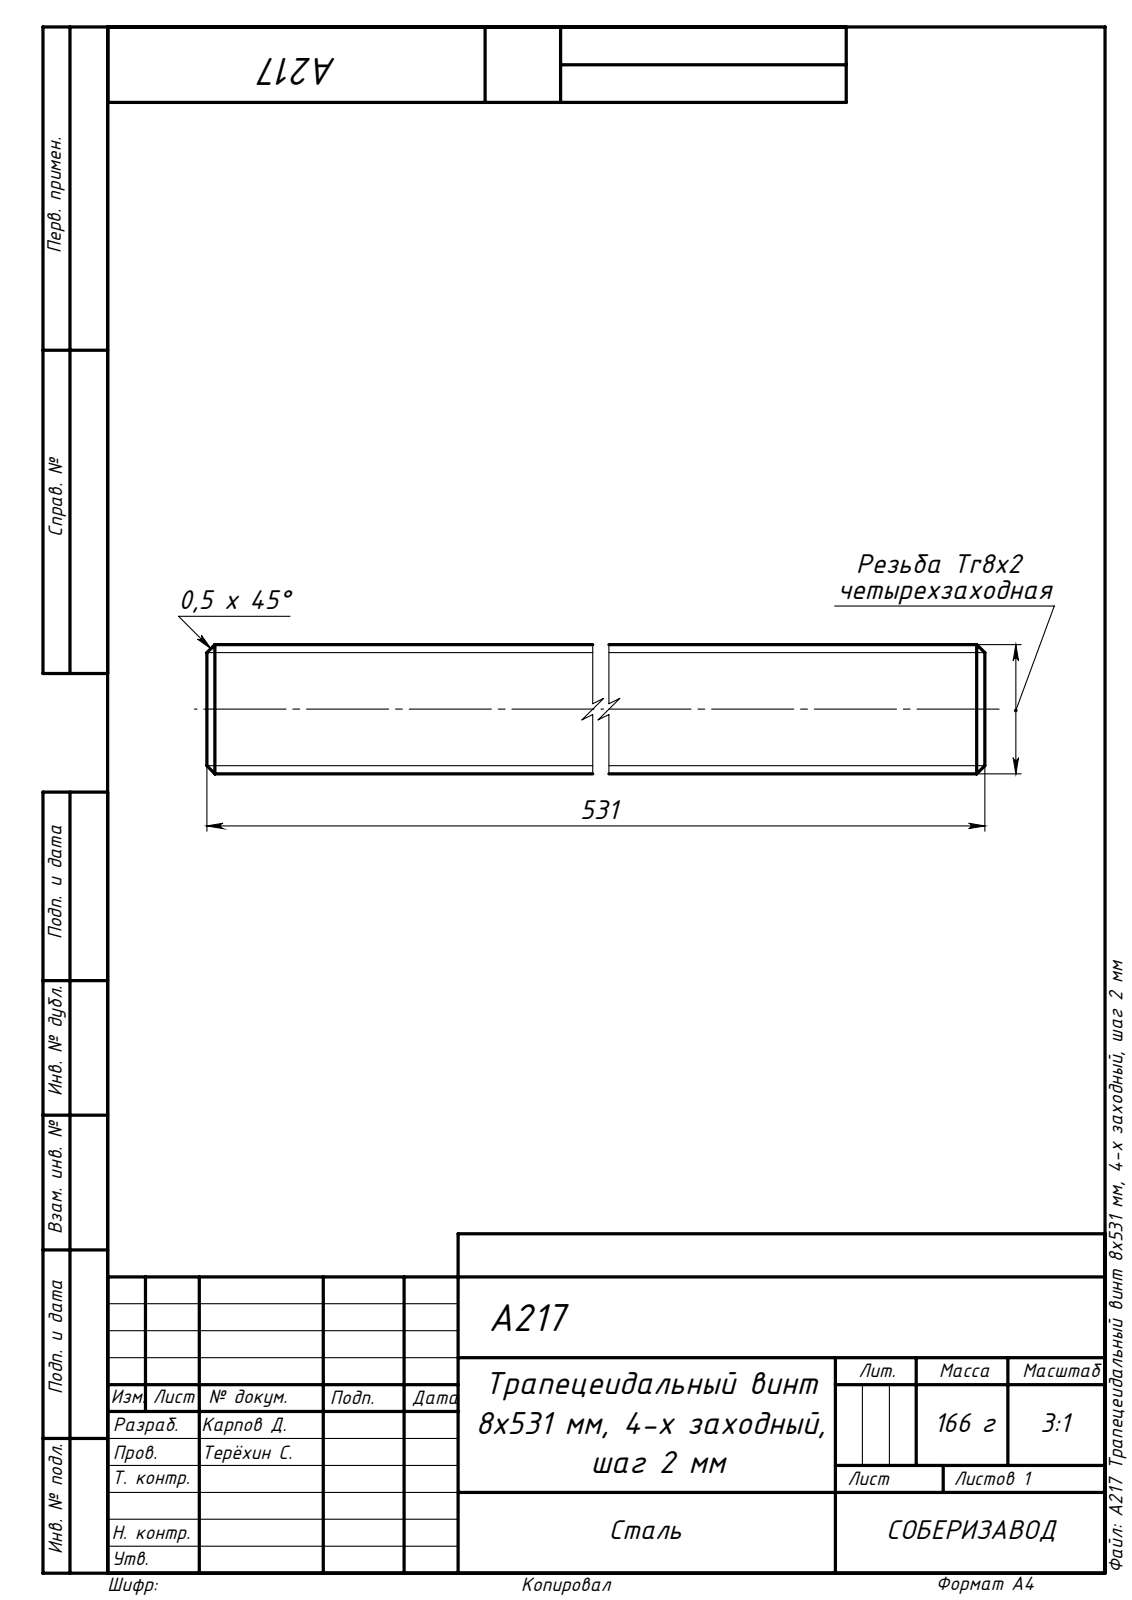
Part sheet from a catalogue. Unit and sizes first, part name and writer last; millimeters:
Units: millimetres
Overall size (bounding box): 531 × 8 × 8
Round bosses / shafts (diameter × count): ⌀8 ×1
Main face-to-face distances: 531
Volume: 26 691 mm³ · Surface area: 13 446 mm²
Bodies: 1 solid, 4 faces (2 planar, 2 cylindrical, 0 other)
Part name (STEP PRODUCT): A217 Трапецеидальный винт 8х531 мм, 4-х заходный, шаг 2 мм
STEP written by: SolidWorks 2018 (AUTOMOTIVE_DESIGN)
